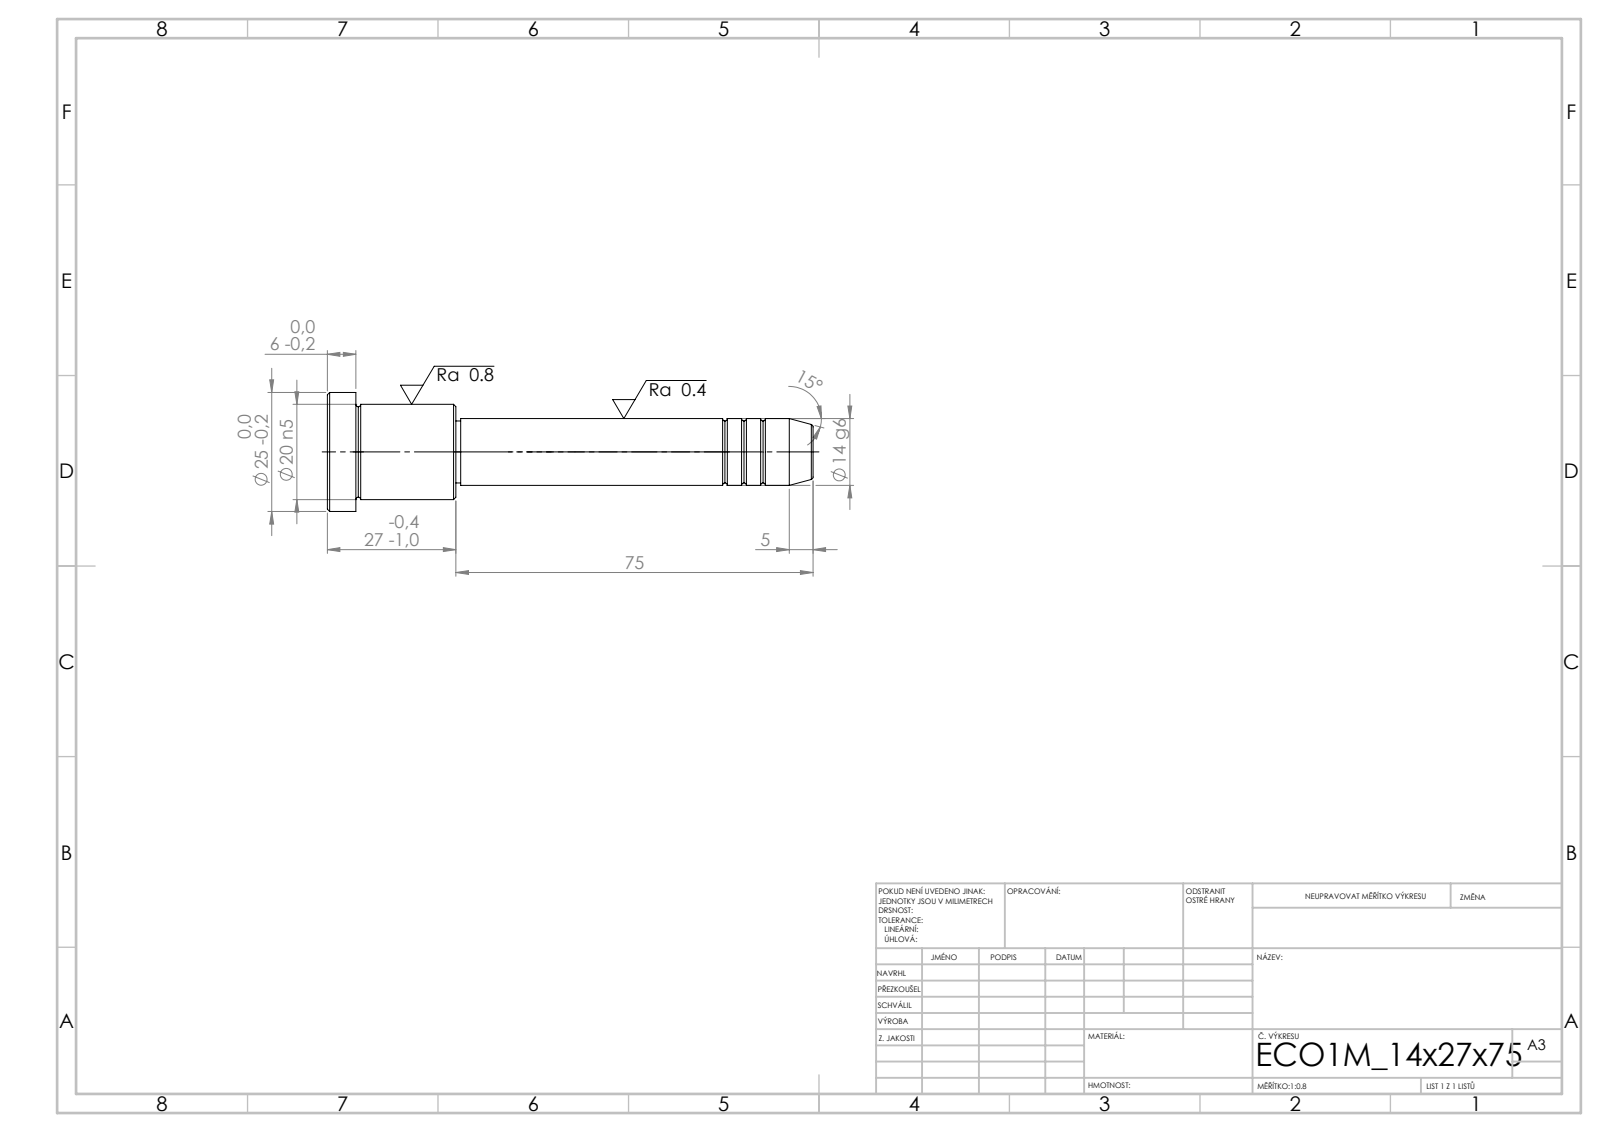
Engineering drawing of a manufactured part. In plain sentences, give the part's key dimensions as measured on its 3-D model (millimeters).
Its 3-D file was written by "SolidWorks 2019 (CONFIG_CONTROL_DESIGN)". It is 1 solid with 43 faces: 5 planar, 14 cylindrical and 24 other. Overall it measures 102 by 25 by 25 millimeters. Its volume is 20 836 cubic millimeters and its surface area 6 096 square millimeters. Round bosses or shafts: 1 of diameter 25, 1 of diameter 20, 1 of diameter 14, 1 of diameter 13. The main face-to-face distances are 6, 21, 27, 75, 96, 102, 74, 1, 22, 28.
